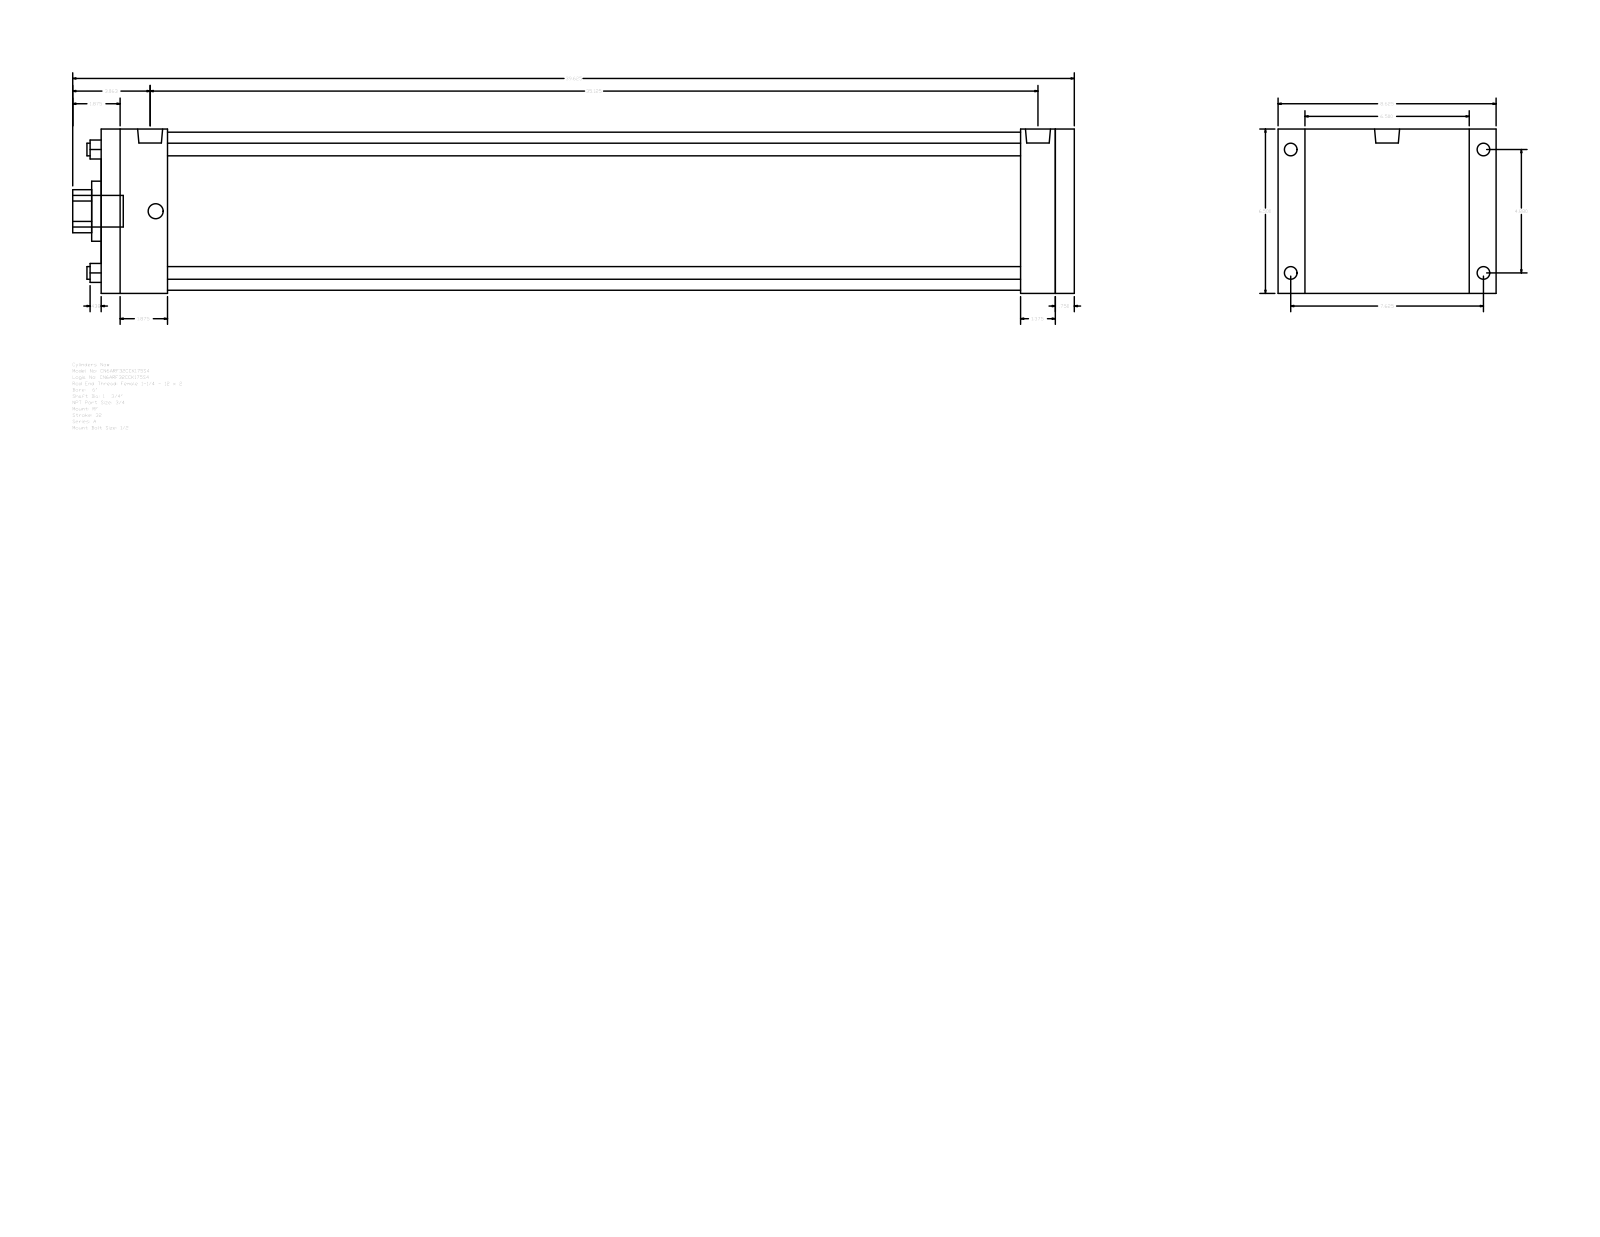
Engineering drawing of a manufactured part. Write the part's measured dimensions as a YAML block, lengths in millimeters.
part_name: "A_RF__0600_1.75"
step_written_by: "GSSL Pune (CONFIG_CONTROL_DESIGN)"
units: millimeters
bodies: {solids: 0, faces: 92, planar: 64, cylindrical: 28, other: 0}
overall_size: [1006.48, 219.07, 165.1]
round_holes:
  - {diameter: 12.7, count: 4}
  - {diameter: 44.45, count: 1}
  - {diameter: 60.33, count: 1}
  - {diameter: 158.75, count: 1}
round_bosses_or_shafts:
  - {diameter: 15.08, count: 4}
  - {diameter: 12.7, count: 4}
  - {diameter: 25.12, count: 2}
  - {diameter: 31.75, count: 1}
partial_cylinders:
  - {radius: 21.63, count: 1}
face_to_face_distances: [165.1, 977.91, 958.85, 19.06, 34.92, 66.68, 892.17, 911.23, 923.93, 857.25]
hole_center_spacings: [87.65, 123.96, 175.31]
